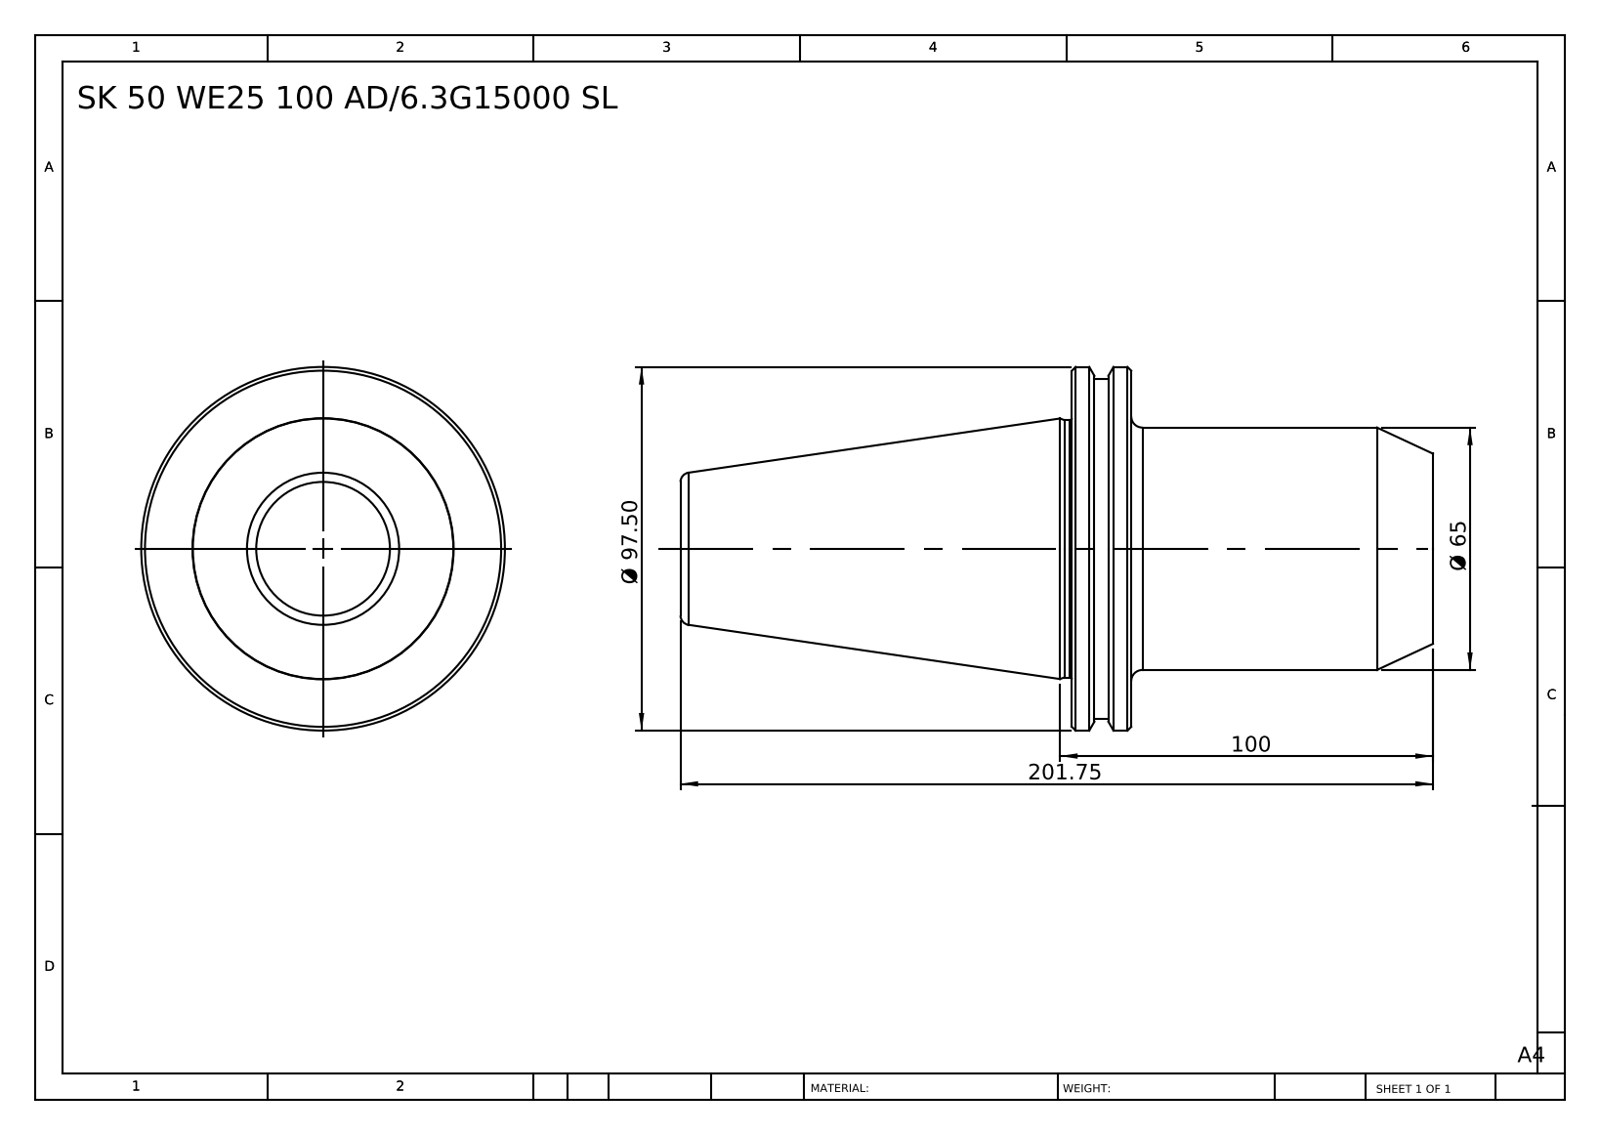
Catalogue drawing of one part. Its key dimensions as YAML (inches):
part_name: "SK50 WE25 100 AD-6.3G15000 SL"
step_written_by: "SolidWorks 2014 (CONFIG_CONTROL_DESIGN)"
units: inches
bodies: {solids: 1, faces: 36, planar: 6, cylindrical: 10, other: 20}
overall_size: [7.943, 3.839, 3.839]
volume: 38.59
surface_area: 79.78
round_bosses_or_shafts:
  - {diameter: 3.839, count: 1}
  - {diameter: 3.583, count: 1}
  - {diameter: 2.717, count: 1}
  - {diameter: 2.559, count: 1}
face_to_face_distances: [0.626, 3.185, 3.811, 7.943, 4.758, 4.132, 3.426, 0.241, 0.385, 4.517]
